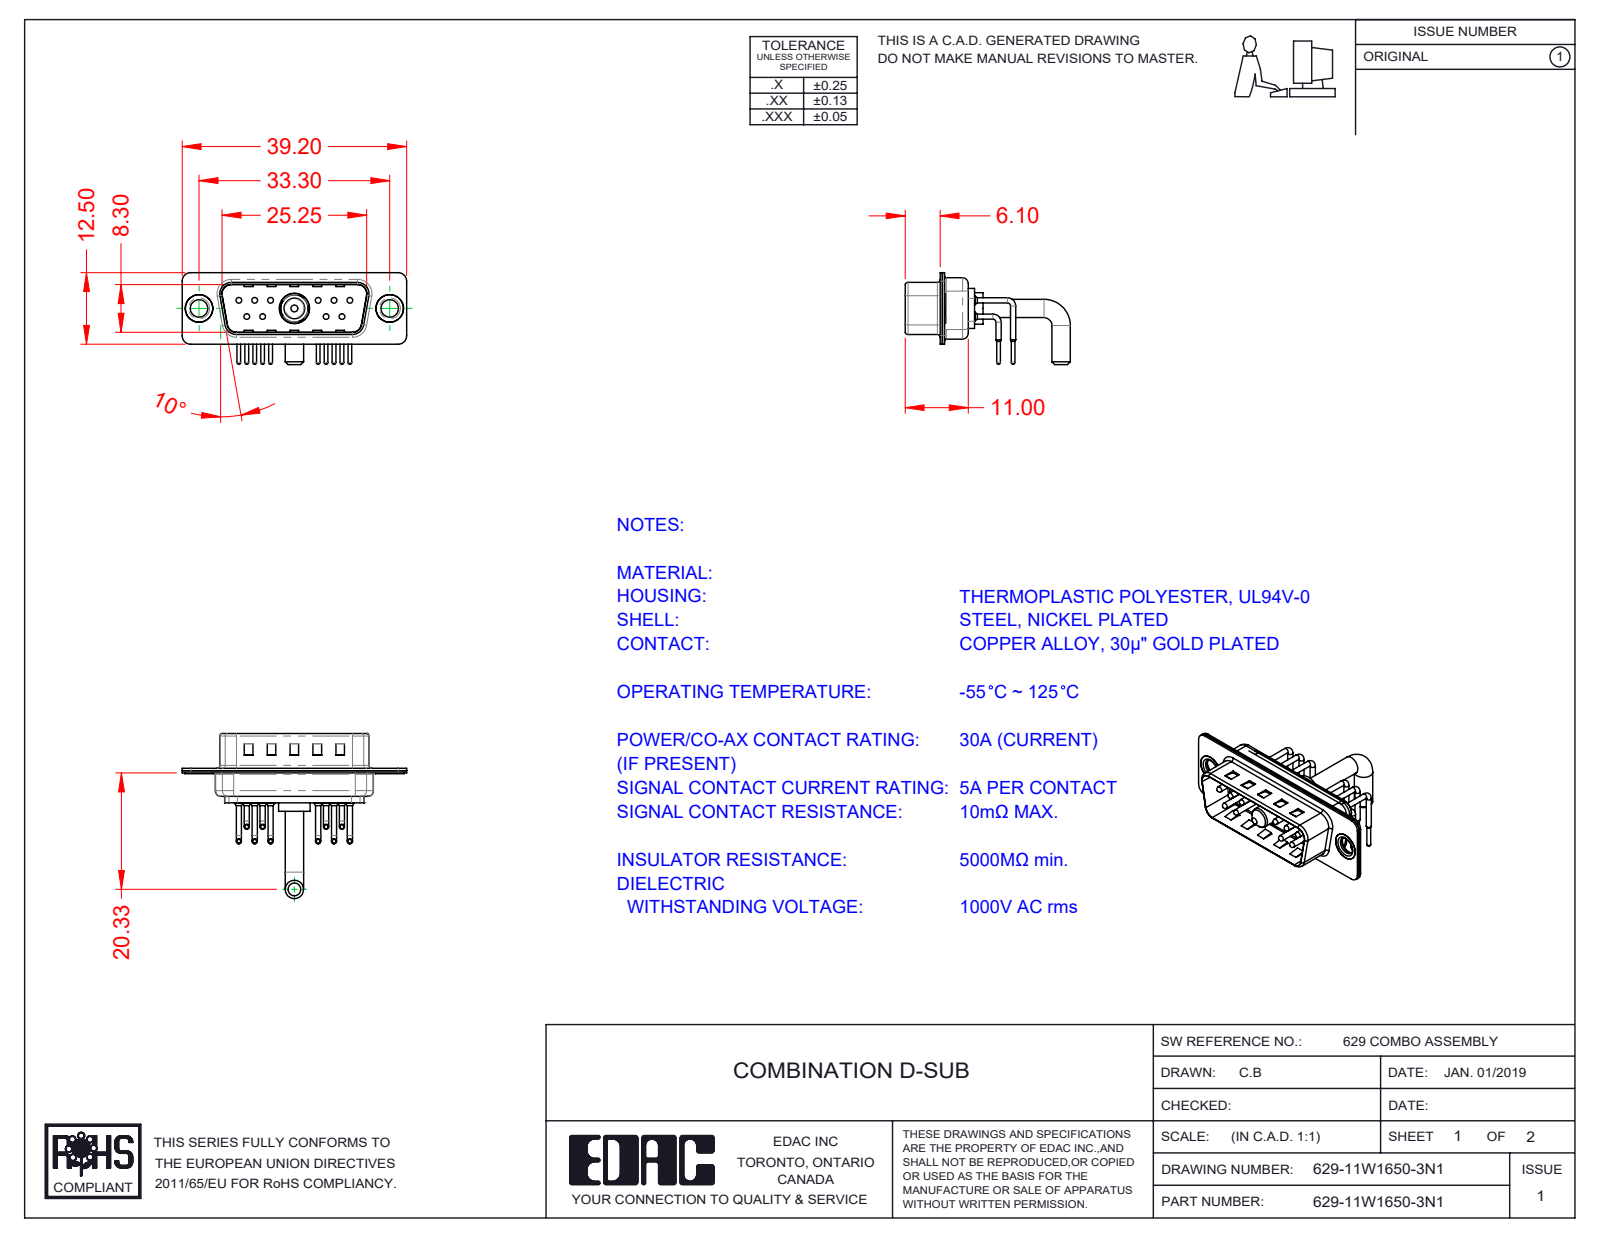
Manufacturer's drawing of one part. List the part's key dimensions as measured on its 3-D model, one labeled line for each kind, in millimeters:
Part name (STEP PRODUCT): 629Combo Housing_11W1; Power Pin_Ext 30A RA; 629Combo Contact Row 1; 629Combo Shell Front_15 Contacts (+4 more)
STEP written by: SolidWorks 2020 (CONFIG_CONTROL_DESIGN)
Units: millimetres
Bodies: 17 solids, 1470 faces (798 planar, 502 cylindrical, 170 other)
Overall size (bounding box): 39.2 × 28.83 × 16.05
Volume: 2 071 mm³ · Surface area: 5 178 mm²
Round holes (diameter × count): ⌀0.75 ×10, ⌀1.6 ×10, ⌀2 ×10, ⌀3.05 ×2, ⌀4 ×2, ⌀4.8 ×2, ⌀4.85 ×1, ⌀5.3 ×1
Round bosses / shafts (diameter × count): ⌀0.9 ×20, ⌀1.5 ×10, ⌀1 ×10, ⌀0.65 ×10, ⌀5 ×2, ⌀4.9 ×2, ⌀3.55 ×2, ⌀3.2 ×2
Partial cylindrical surfaces — rounded edges, fillets, slot ends (radius × count): R1.5 ×16, R2 ×12, R1.01 ×10, R0.5 ×8, R1.6 ×8, R1 ×7, R0.25 ×4, R0.6 ×4
Main face-to-face distances: 0.4, 0.8, 9.5, 9.1, 8.7, 9.9, 0.75, 5.6, 1.2, 0.35
Hole centre spacings: 3.16, 2.77, 13.85, 11.08, 16.62, 5.03, 5.04, 5.54
